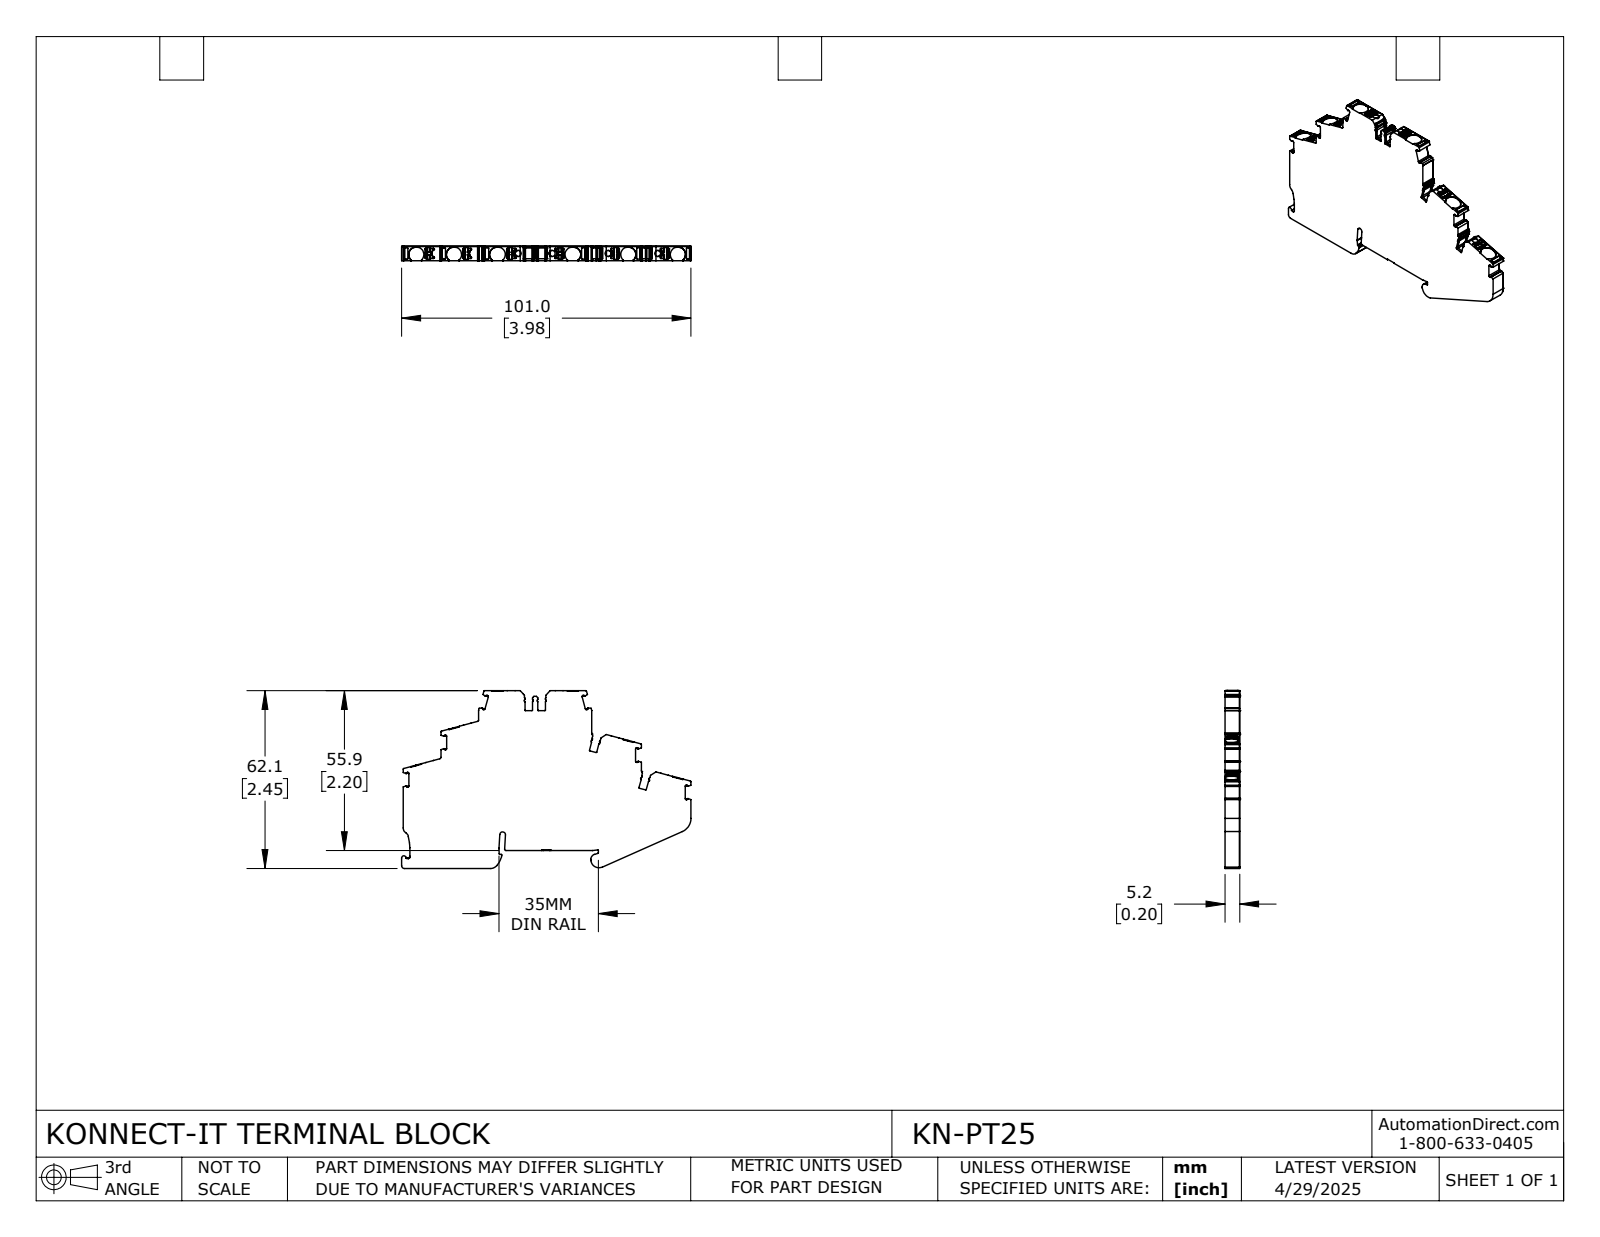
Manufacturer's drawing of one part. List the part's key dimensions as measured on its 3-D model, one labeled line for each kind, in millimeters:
Part name (STEP PRODUCT): KN-PT25
STEP written by: SolidWorks 2024 (CONFIG_CONTROL_DESIGN)
Units: millimetres
Bodies: 1 solid, 1212 faces (579 planar, 528 cylindrical, 105 other)
Overall size (bounding box): 101 × 62.1 × 5.2
Volume: 22 190 mm³ · Surface area: 10 810 mm²
Round holes (diameter × count): ⌀2.1 ×4
Partial cylindrical surfaces — rounded edges, fillets, slot ends (radius × count): R0.2 ×128, R0.1 ×49, R0.3 ×47, R0.5 ×26, R0.2 ×24, R0.4 ×17, R0.6 ×14, R0.2 ×12
Main face-to-face distances: 5.2, 6.2, 2, 55.7, 61.9, 8.1, 17.3, 13.2, 62.1, 55.9
Hole centre spacings: 11.8, 20.1
